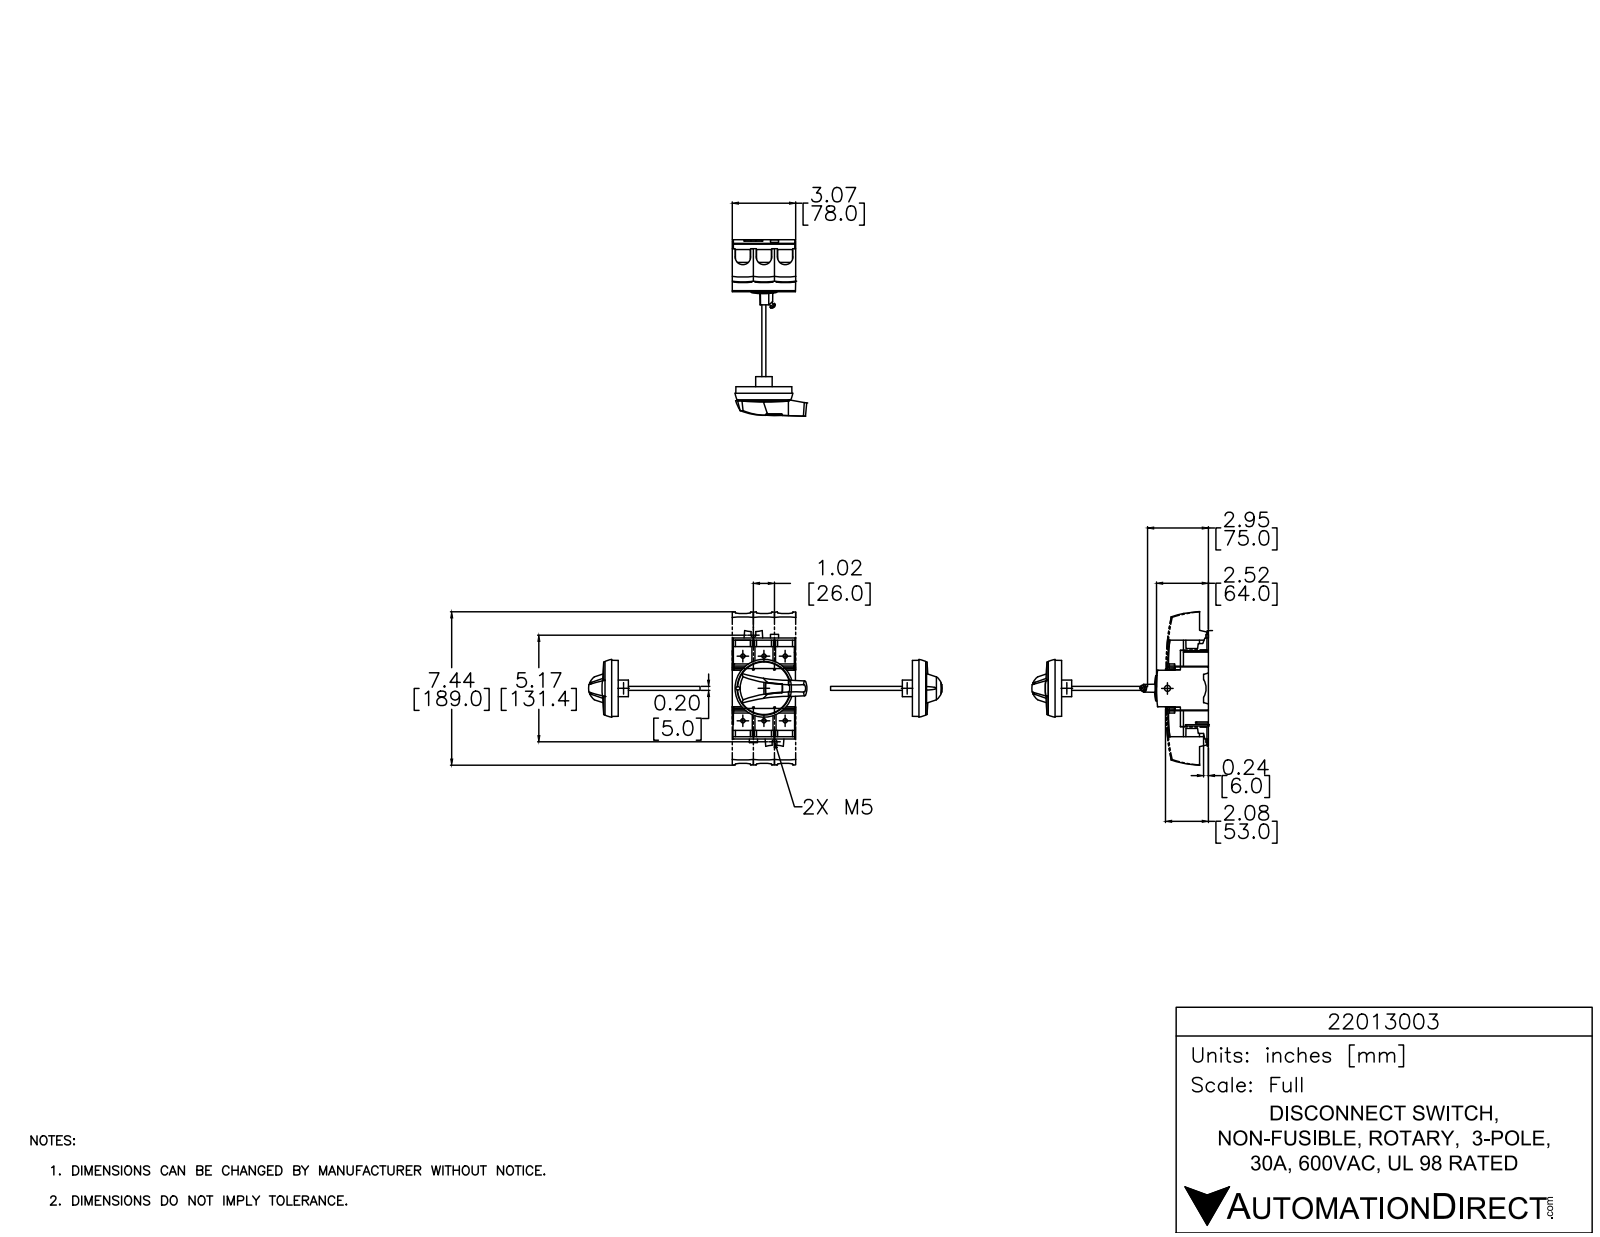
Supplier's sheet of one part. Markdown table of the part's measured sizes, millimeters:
| quantity | value |
| --- | --- |
| part name | 22013003 |
| STEP written by | SolidWorks 2015 (AUTOMOTIVE_DESIGN) |
| units | millimeters |
| bodies | 1 solid, 274 faces (210 planar, 45 cylindrical, 19 other) |
| overall size | 142.7 × 78.8 × 64 |
| volume | 457 500 mm³ |
| surface area | 53 740 mm² |
| round holes (diameter × count) | 5.2 × 6, 7.2 × 1, 9.3 × 1, 32 × 1 |
| round bosses / shafts (diameter × count) | 20.2 × 1 |
| partial cylindrical surfaces (radius × count) | 90 × 3, 92.6 × 3, 2.9 × 2, 42.5 × 2 |
| main face-to-face distances | 77.8, 26, 7.9, 111, 1.1, 76.7, 2.5, 28.5, 46.9, 20.9 |
| hole center spacings | 26, 83.7, 79.6, 47.5, 47.5, 52, 95, 39.8 |
